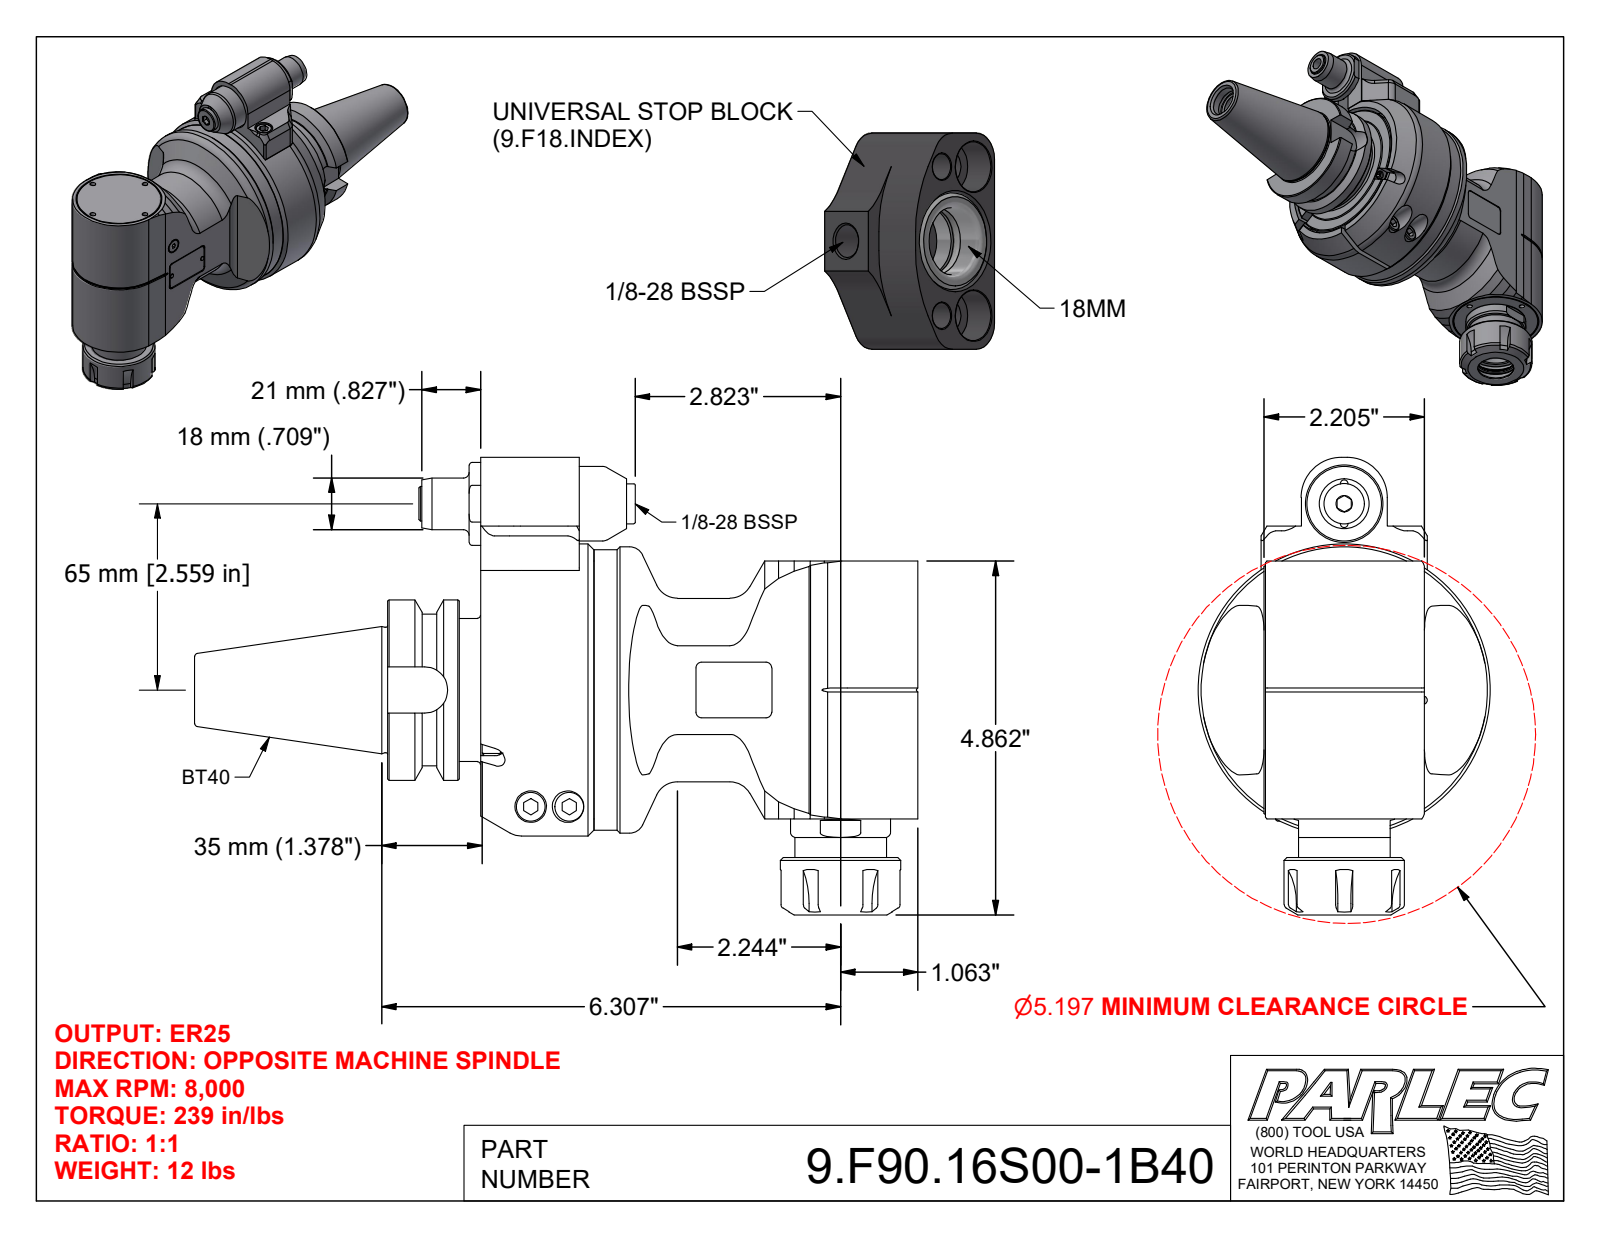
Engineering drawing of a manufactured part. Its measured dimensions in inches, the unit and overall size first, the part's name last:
Units: inches
Overall size (bounding box): 9.945 × 6.289 × 4.016
Round holes (diameter × count): ⌀0.126 ×4, ⌀0.102 ×2, ⌀0.165 ×2, ⌀0.197 ×2, ⌀0.409 ×2, ⌀0.433 ×2, ⌀1.063 ×2, ⌀0.098 ×1, ⌀0.118 ×1, ⌀0.256 ×1, ⌀0.276 ×1, ⌀0.335 ×1
Round bosses / shafts (diameter × count): ⌀0.394 ×4, ⌀0.236 ×4, ⌀0.709 ×2, ⌀0.315 ×2, ⌀0.098 ×2, ⌀4.016 ×1, ⌀3.937 ×1, ⌀3.858 ×1
Partial cylindrical surfaces — rounded edges, fillets, slot ends (radius × count): R0.079 ×12, R0.984 ×6, R0.157 ×4, R0.016 ×2, R0.02 ×2, R0.039 ×2, R0.138 ×2, R0.197 ×2
Main face-to-face distances: 1.26, 1.555, 0.295, 0.02, 1.252, 0.315, 1.28, 0.276, 0.303, 0.039
Hole centre spacings: 0.846, 1.197, 0.276, 1.693, 0.512, 0.551, 1.72, 2.283
Volume: 61.71 in³ · Surface area: 226.5 in²
Bodies: 5 solids, 529 faces (244 planar, 129 cylindrical, 156 other)
Part name (STEP PRODUCT): 9.F90.16S00-1B40; 9_F90_16S00; 9_GA1_346_2 (Type 1, BT40, 65mm)
STEP written by: Autodesk Inventor 2022 (AUTOMOTIVE_DESIGN)
